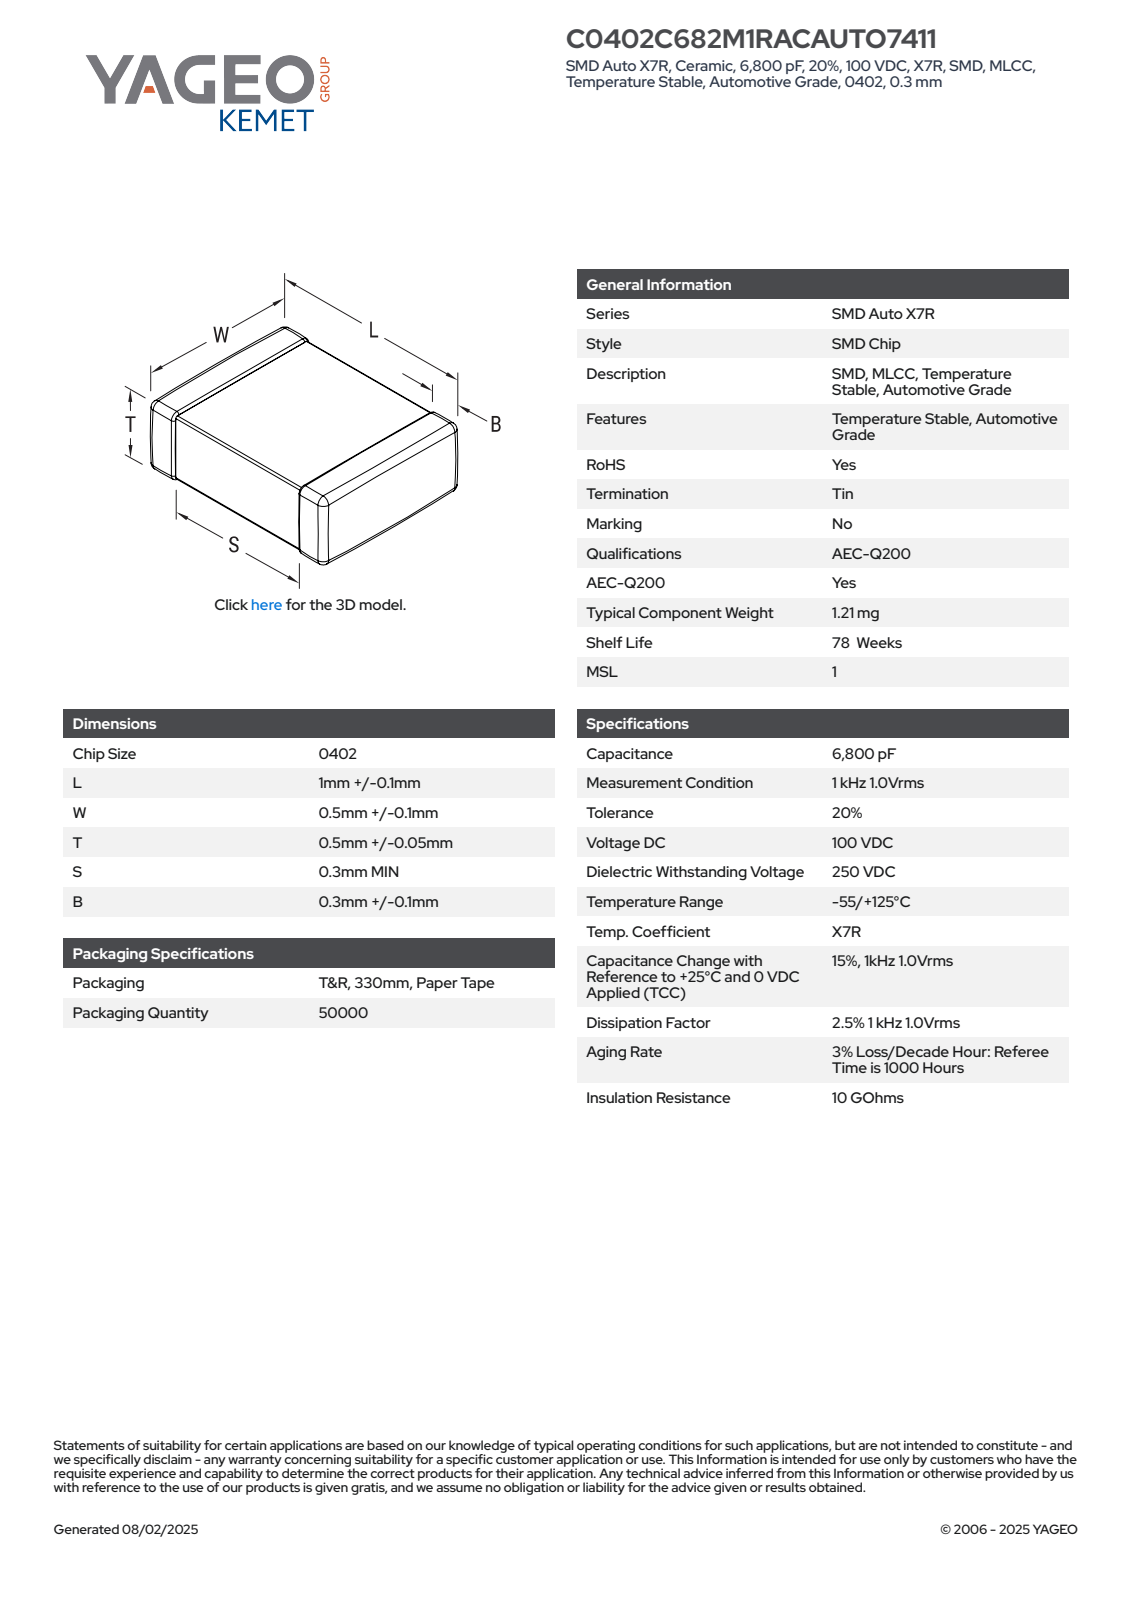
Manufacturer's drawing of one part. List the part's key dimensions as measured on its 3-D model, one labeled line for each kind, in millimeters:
Part name (STEP PRODUCT): CCS_CCSTD_0402_L1.1W0.6T0.55B0.3
STEP written by: SolidWorks 2021 (AUTOMOTIVE_DESIGN)
Units: millimetres
Bodies: 4 solids, 125 faces (71 planar, 38 cylindrical, 16 other)
Overall size (bounding box): 1.1 × 0.6 × 0.55
Volume: 0.354 mm³ · Surface area: 3 mm²
Main face-to-face distances: 0.55, 0.6, 0.54, 0.59, 1.1, 0.53, 0.58, 0.51, 0.52, 0.56
